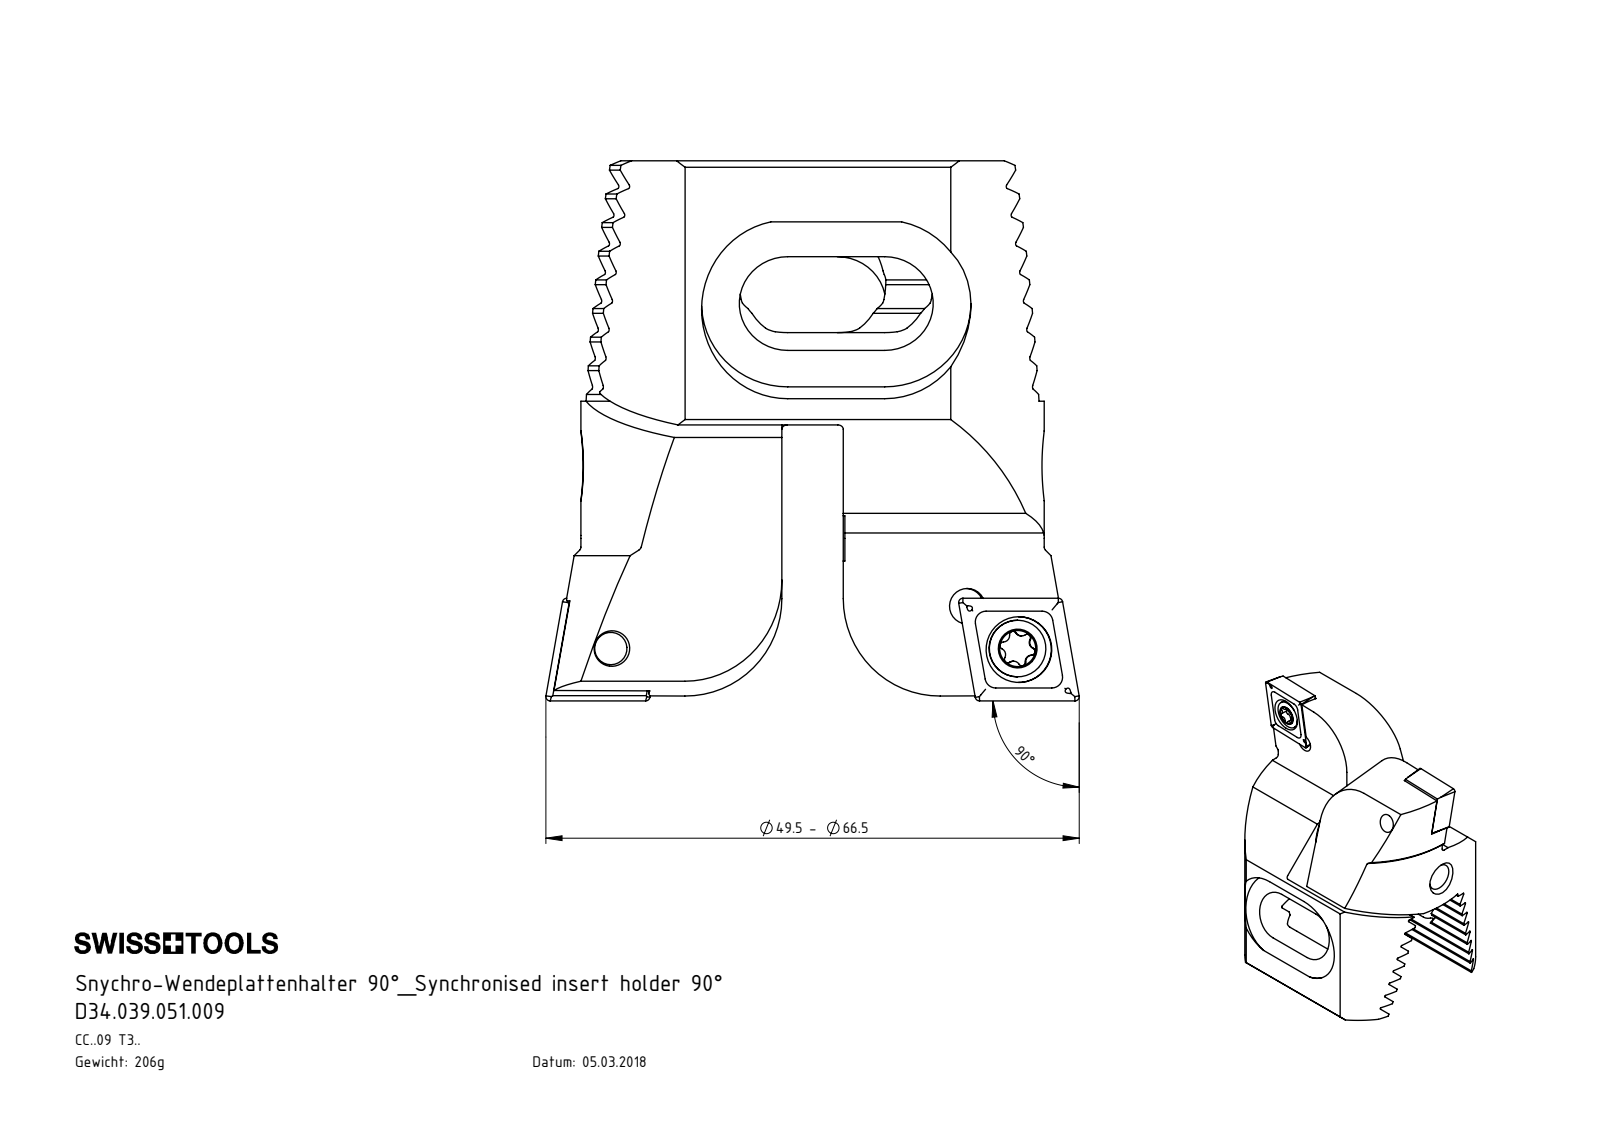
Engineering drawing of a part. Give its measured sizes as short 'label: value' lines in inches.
name: CCMT09T304; ISO 4026 - M3 x 5; Z42-ER3.001.040_A; WCB-ER2.001.009_A (+4 more)
written by: SolidWorks 2017 (CONFIG_CONTROL_DESIGN)
unit: in
bodies: 11 solids, 525 faces (205 planar, 170 cylindrical, 150 other)
size: 1.972 × 1.949 × 1.346
volume: 1.705 in³; area: 22.57 in²
holes: 7× ⌀0.13, 2× ⌀0.039, 2× ⌀0.173, 2× ⌀0.24, 1× ⌀0.197
bosses: 3× ⌀0.118, 2× ⌀0.207, 2× ⌀0.157, 1× ⌀0.669, 1× ⌀0.236, 1× ⌀0.15
rounds: 16× R0.008, 12× R0.013, 12× R0.023, 8× R0.039, 4× R0.02, 4× R0.177, 4× R0.315, 2× R0.354
face distances: 0.094, 0.187, 0.469, 0.375, 0.563, 0.281, 0.196, 0.281, 0.041, 0.656
hole spacings: 0.24, 0.512, 1.322, 0.246, 0.246, 0.989, 1.13, 1.327
